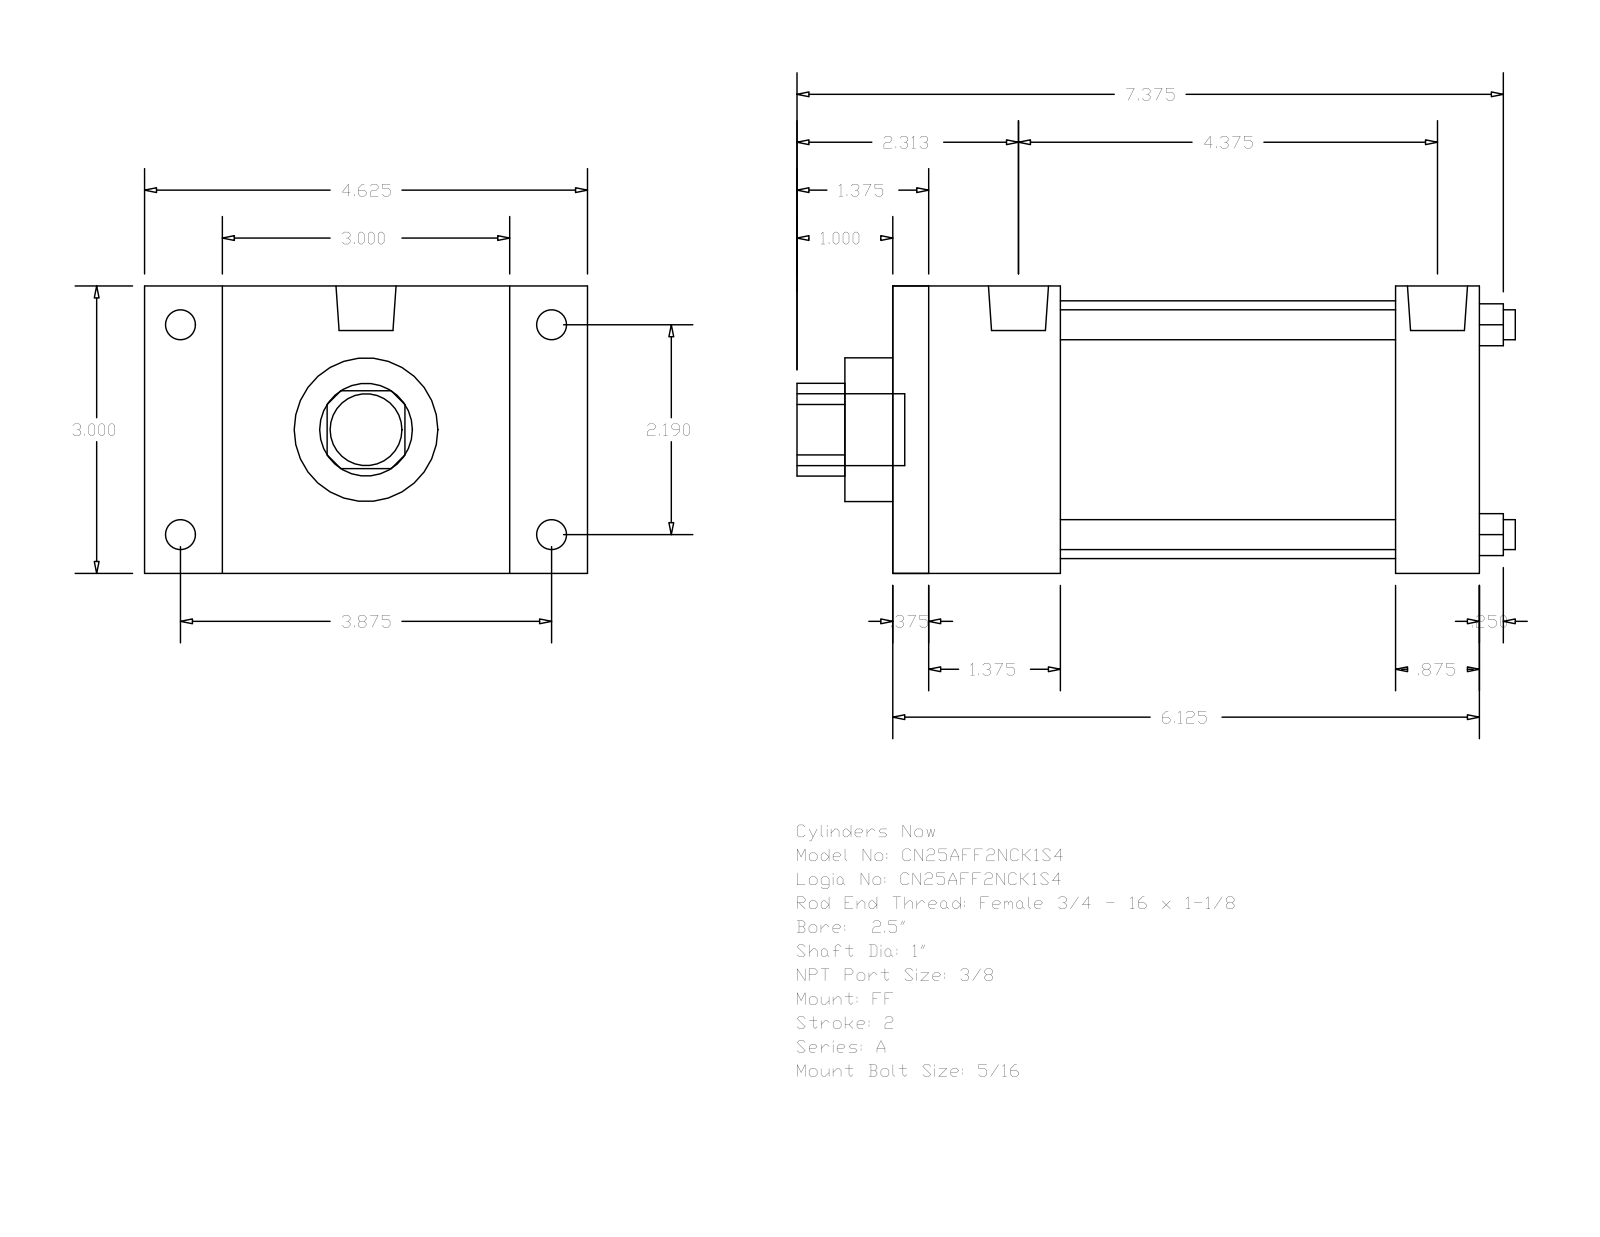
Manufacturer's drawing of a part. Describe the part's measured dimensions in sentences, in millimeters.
The part is named "A_FF__0250_1". Its 3-D file was written by "GSSL Pune (CONFIG_CONTROL_DESIGN)". It is 0 solids with 92 faces: 64 planar, 28 cylindrical and 0 other. Overall it measures 190.5 by 117.47 by 76.2 millimeters. Round holes: 4 of diameter 7.94, 1 of diameter 25.4, 1 of diameter 38.1, 1 of diameter 68.33. Round bosses or shafts: 4 of diameter 7.94, 4 of diameter 5.56, 2 of diameter 15.93, 1 of diameter 19.05. Partial cylindrical surfaces (rounded edges, fillets, slot ends): 1 of radius 12.29. The main face-to-face distances are 76.2, 155.57, 146.05, 9.52, 22.22, 44.45, 133.35, 34.93, 123.83, 88.9. The hole center spacings are 39.33, 55.62, 78.66.
